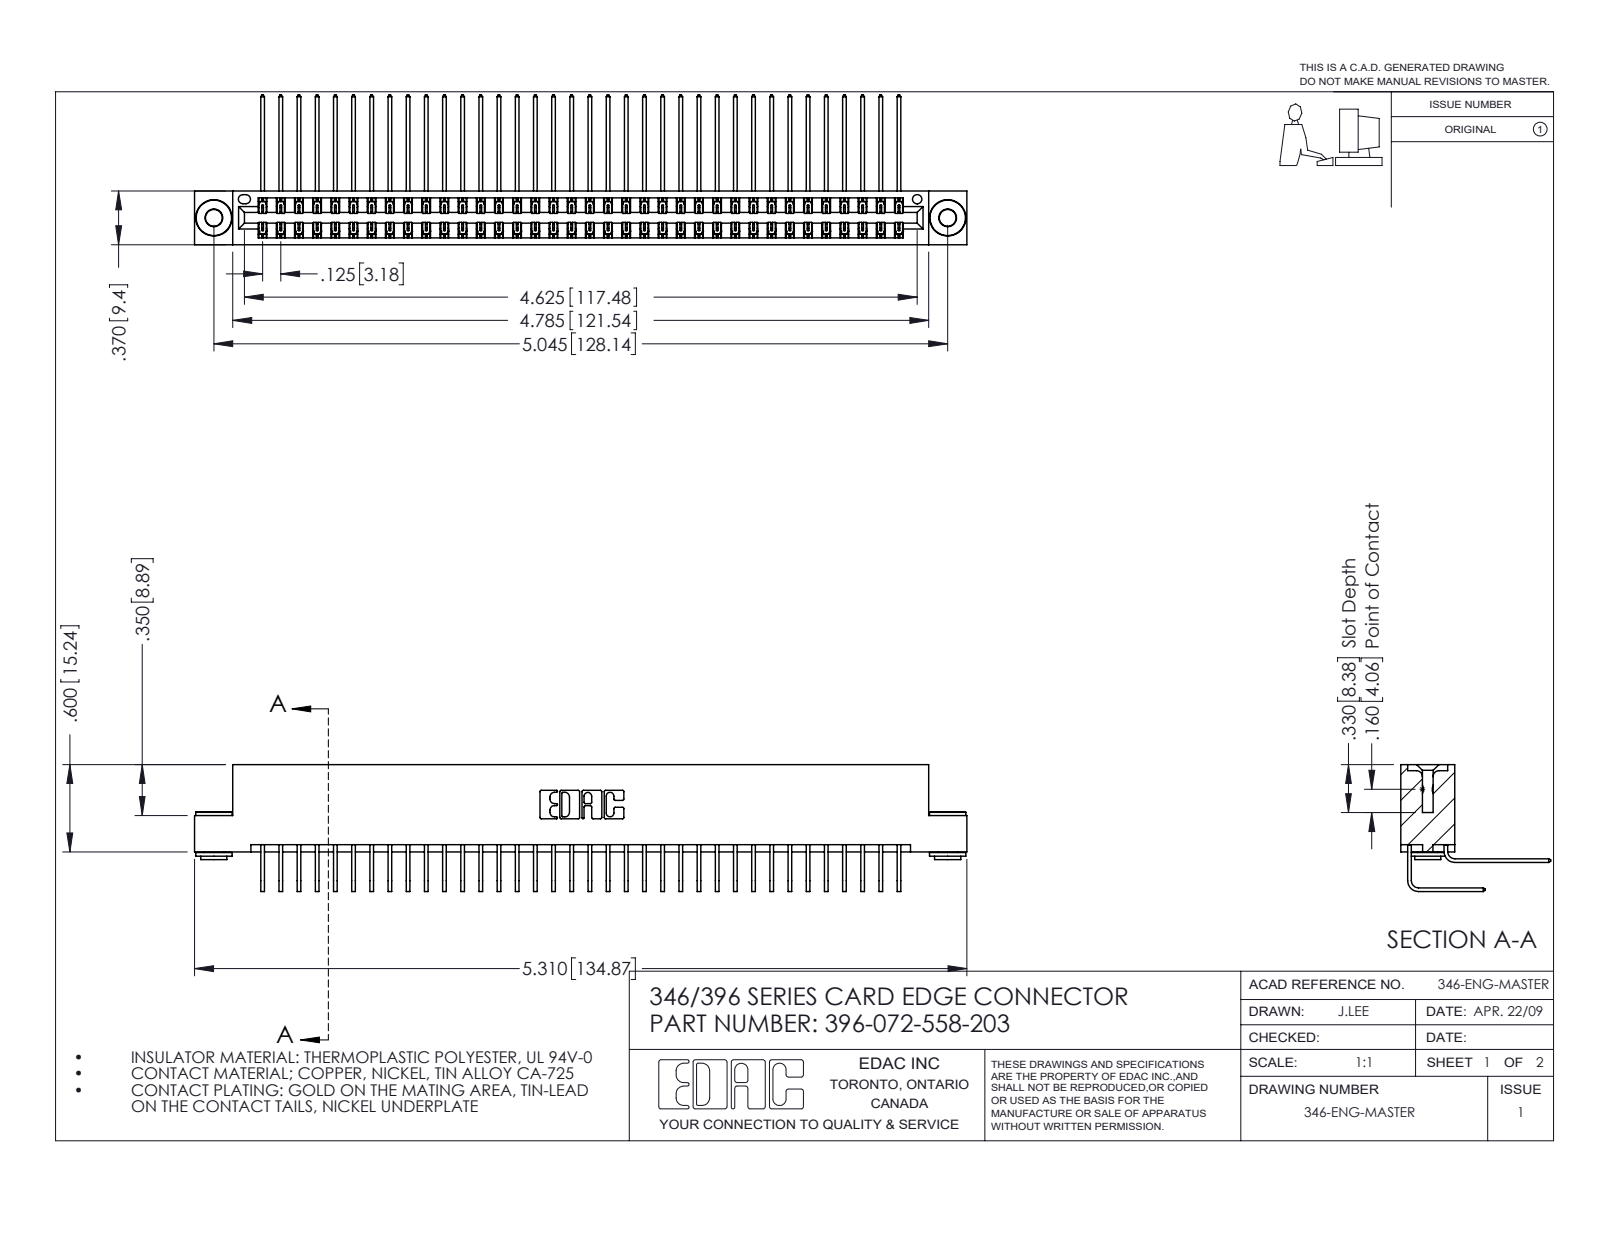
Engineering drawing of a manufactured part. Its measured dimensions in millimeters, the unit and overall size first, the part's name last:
Units: millimetres
Overall size (bounding box): 134.9 × 26.2 × 22.2
Round holes (diameter × count): ⌀2.9 ×2, ⌀4 ×2, ⌀1.6 ×1
Round bosses / shafts (diameter × count): ⌀6.4 ×2, ⌀4.6 ×2, ⌀3.5 ×2
Partial cylindrical surfaces — rounded edges, fillets, slot ends (radius × count): R0.2 ×108, R0.3 ×22, R0.2 ×6, R0.8 ×6, R0.7 ×3, R0.4 ×2, R0.6 ×2, R0.6 ×2
Main face-to-face distances: 8.2, 1.2, 0.6, 6.4, 9.4, 7.6, 1.8, 7, 3.8, 5.6
Hole centre spacings: 6.2, 122.8, 128.1
Volume: 13 500 mm³ · Surface area: 20 720 mm²
Bodies: 75 solids, 4048 faces (2750 planar, 1290 cylindrical, 8 other)
Part name (STEP PRODUCT): 396-072-558-203; 345-250-002_345-250-002-102; 345-292-001_558 Tail - 2; 345-292-001_558 559 Tail - 1 (+1 more)
STEP written by: SolidWorks 2016 (CONFIG_CONTROL_DESIGN)
